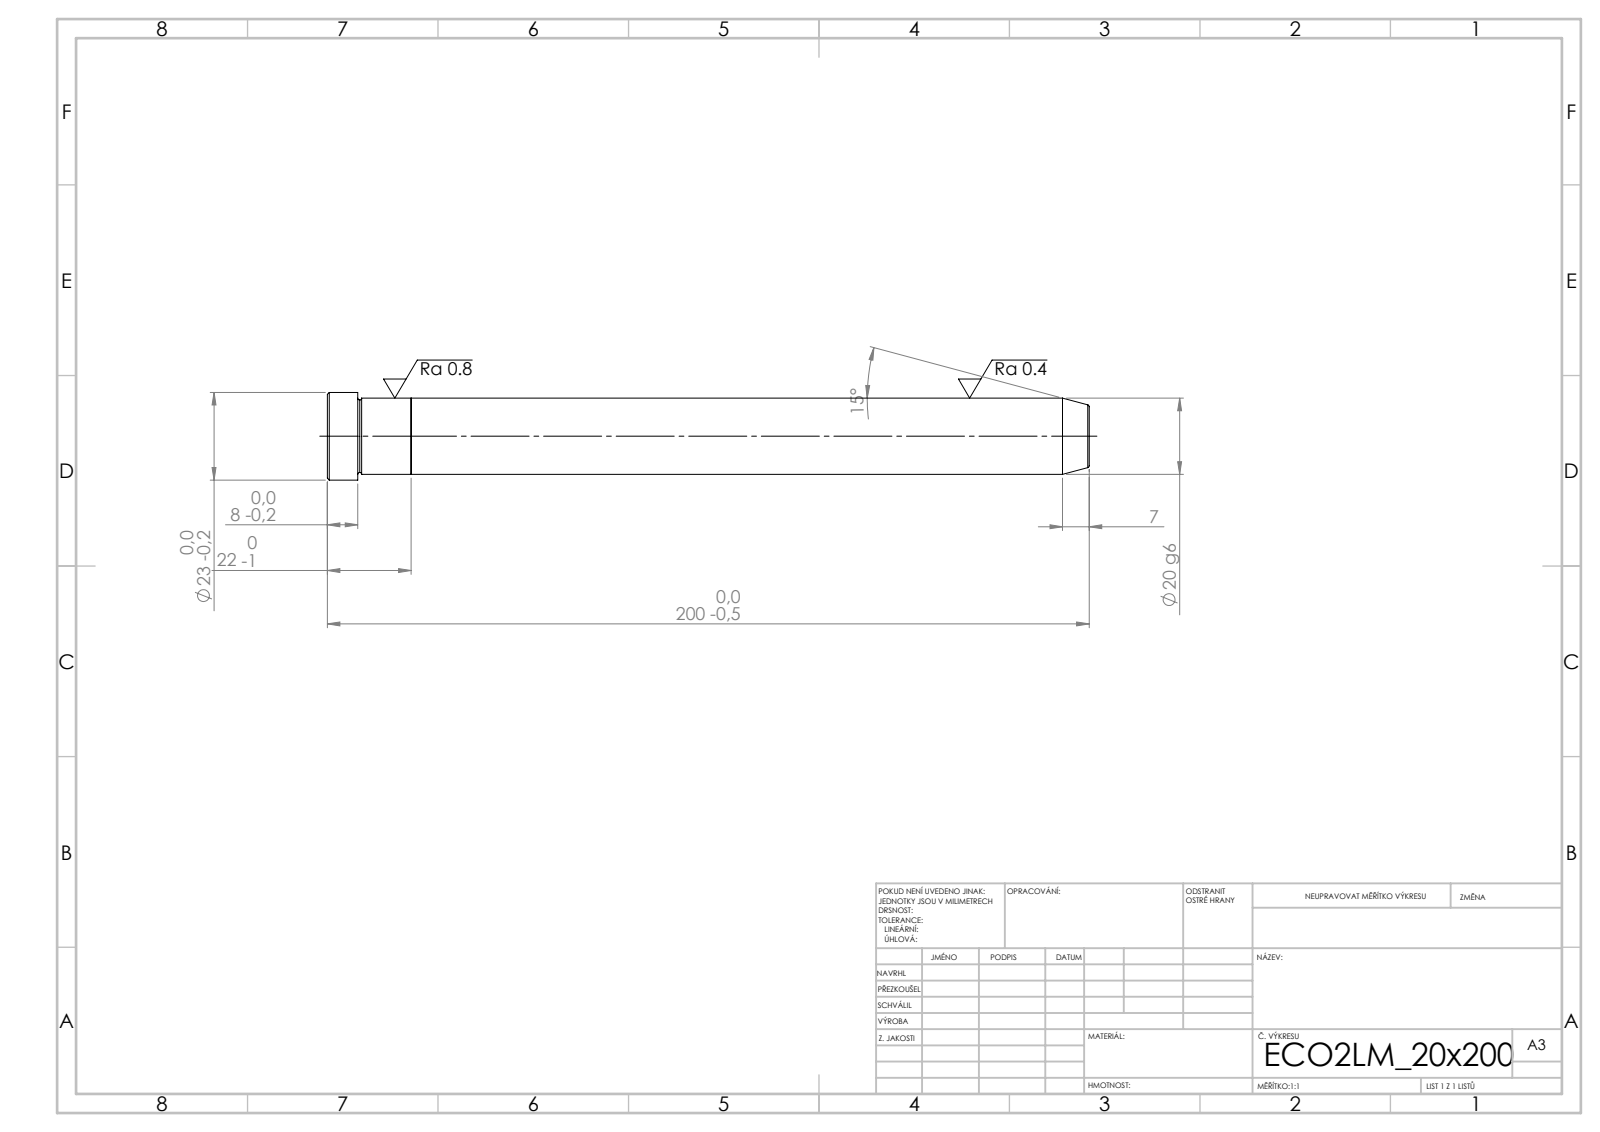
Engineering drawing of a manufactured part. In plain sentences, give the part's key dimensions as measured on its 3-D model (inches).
Its 3-D file was written by "SolidWorks 2019 (CONFIG_CONTROL_DESIGN)". It is 2 solids with 21 faces: 5 planar, 6 cylindrical and 10 other. Overall it measures 7.874 by 0.906 by 0.906 inches. Its volume is 3.858 cubic inches and its surface area 21.66 square inches. Round bosses or shafts: 1 of diameter 0.906, 1 of diameter 0.787. The main face-to-face distances are 0.866, 7.008, 7.874, 7.559, 0.551, 0.315.
